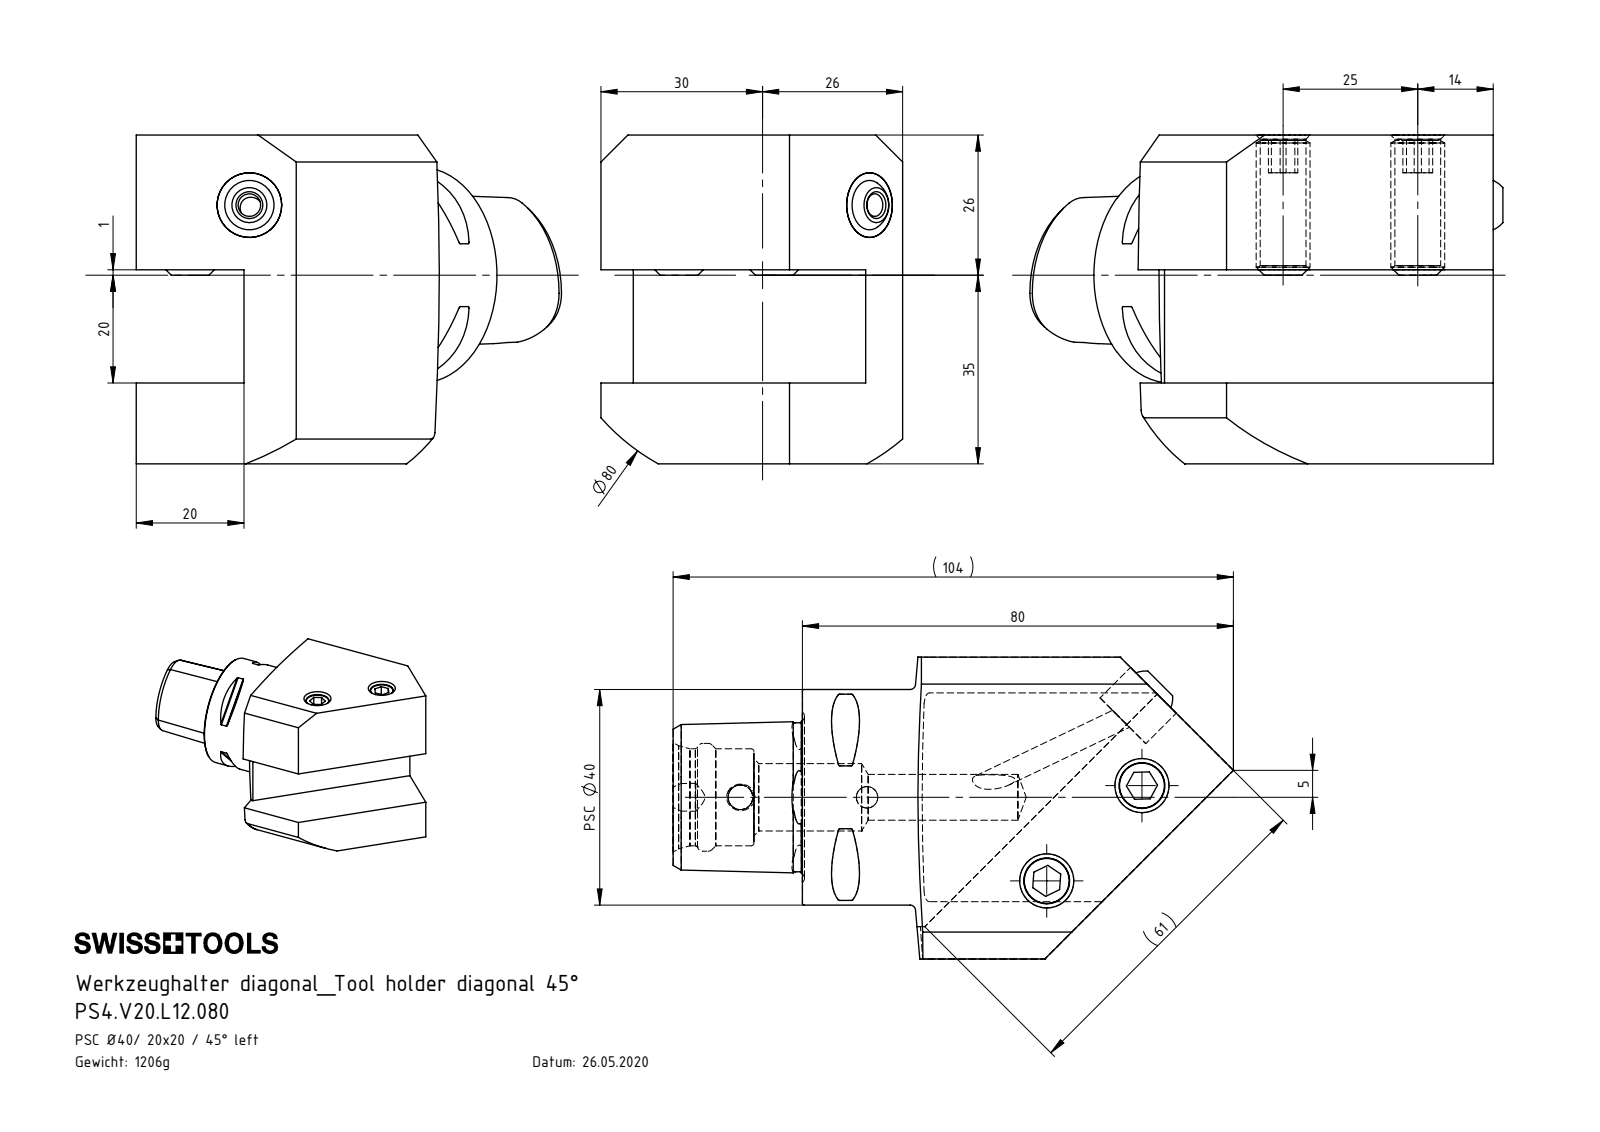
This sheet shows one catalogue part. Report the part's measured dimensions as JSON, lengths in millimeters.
{"part_name": "KU1-U12.001.010; PS4-V20.L12.080_A; KU1-U12.001.010_2; KU1-U12.001.010_1 (+2 more)", "step_written_by": "SolidWorks 2017 (AUTOMOTIVE_DESIGN)", "units": "millimeters", "bodies": {"solids": 5, "faces": 153, "planar": 54, "cylindrical": 29, "other": 70}, "overall_size": [104, 61, 56], "volume_mm3": 153960, "surface_area_mm2": 29612, "round_holes": [[8.5, 3], [4.2, 2], [4, 1], [4.6, 1], [7, 1], [12, 1], [12.5, 1], [18, 1], [20, 1]], "round_bosses_or_shafts": [[10, 2], [40, 1]], "partial_cylinders_radius": [[0.3, 8], [3, 1], [40, 1]], "face_to_face_distances": [61, 20, 15, 46, 25, 36, 21, 56, 24, 8], "hole_center_spacings": [23.5, 25, 36.78, 51.08, 58.93, 74.56]}
